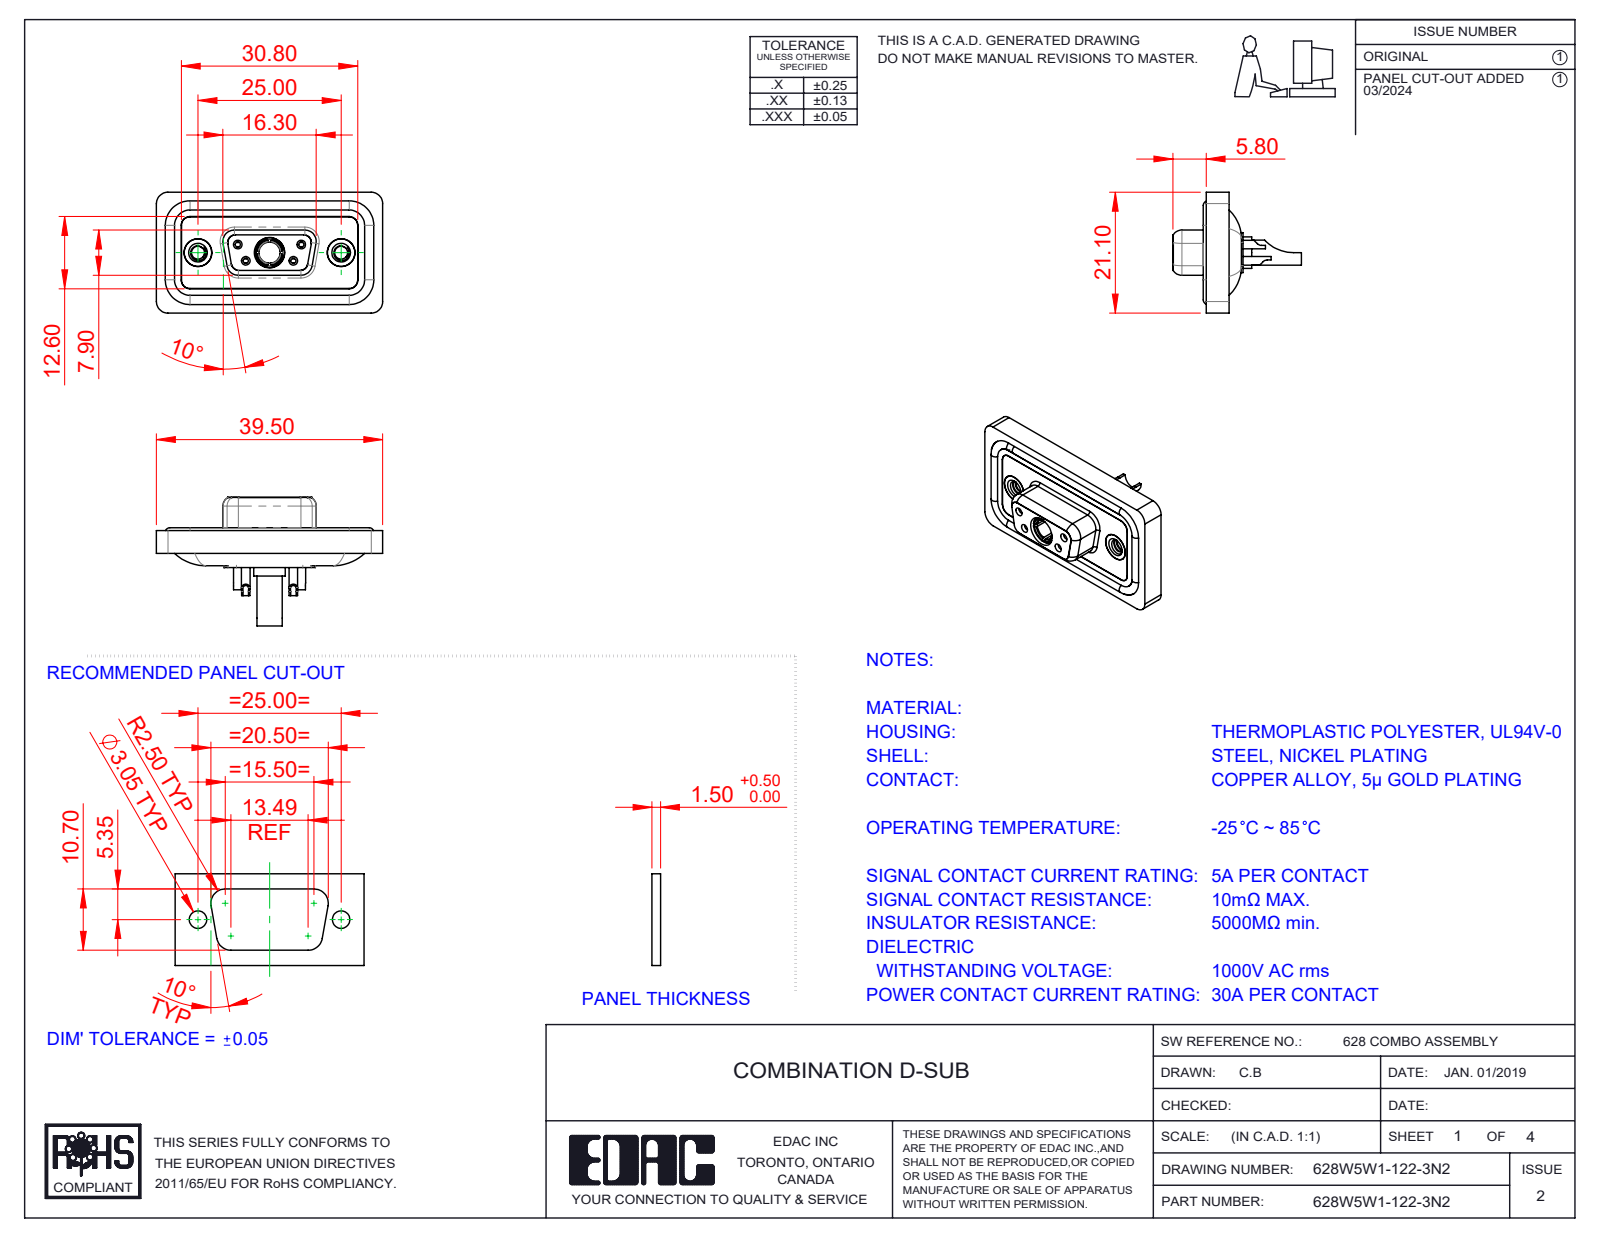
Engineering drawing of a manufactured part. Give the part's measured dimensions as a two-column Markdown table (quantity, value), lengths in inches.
| quantity | value |
| --- | --- |
| part name | 628Combo Contact Row 2_22; 628Combo Shell Front_09 Contacts; 628Combo Threaded Rivet_2; 628Combo Housing_5W1 (+5 more) |
| STEP written by | SolidWorks 2023 (CONFIG_CONTROL_DESIGN) |
| units | inches |
| bodies | 13 solids, 686 faces (205 planar, 298 cylindrical, 183 other) |
| overall size | 1.555 × 0.884 × 0.831 |
| volume | 0.293 in³ |
| surface area | 12.07 in² |
| round holes (diameter × count) | 0.035 × 4, 0.039 × 4, 0.043 × 4, 0.059 × 4, 0.079 × 4, 0.191 × 3, 0.063 × 2, 0.067 × 2, 0.089 × 2, 0.157 × 2, 0.159 × 2, 0.197 × 2 |
| round bosses / shafts (diameter × count) | 0.063 × 6, 0.087 × 4, 0.195 × 2, 0.189 × 2, 0.217 × 1, 0.205 × 1, 0.195 × 1, 0.187 × 1 |
| partial cylindrical surfaces (radius × count) | 0.059 × 22, 0.079 × 18, 0.053 × 8, 0.063 × 8, 0.039 × 6, 0.01 × 4, 0.02 × 4, 0.024 × 4 |
| main face-to-face distances | 0.016, 0.114, 0.043, 0.071, 0.063, 0.02, 0.222, 0.293, 0.211, 0.142 |
| hole center spacings | 0.124, 0.225, 0.28, 0.492, 0.713, 0.173, 0.173, 0.327 |
